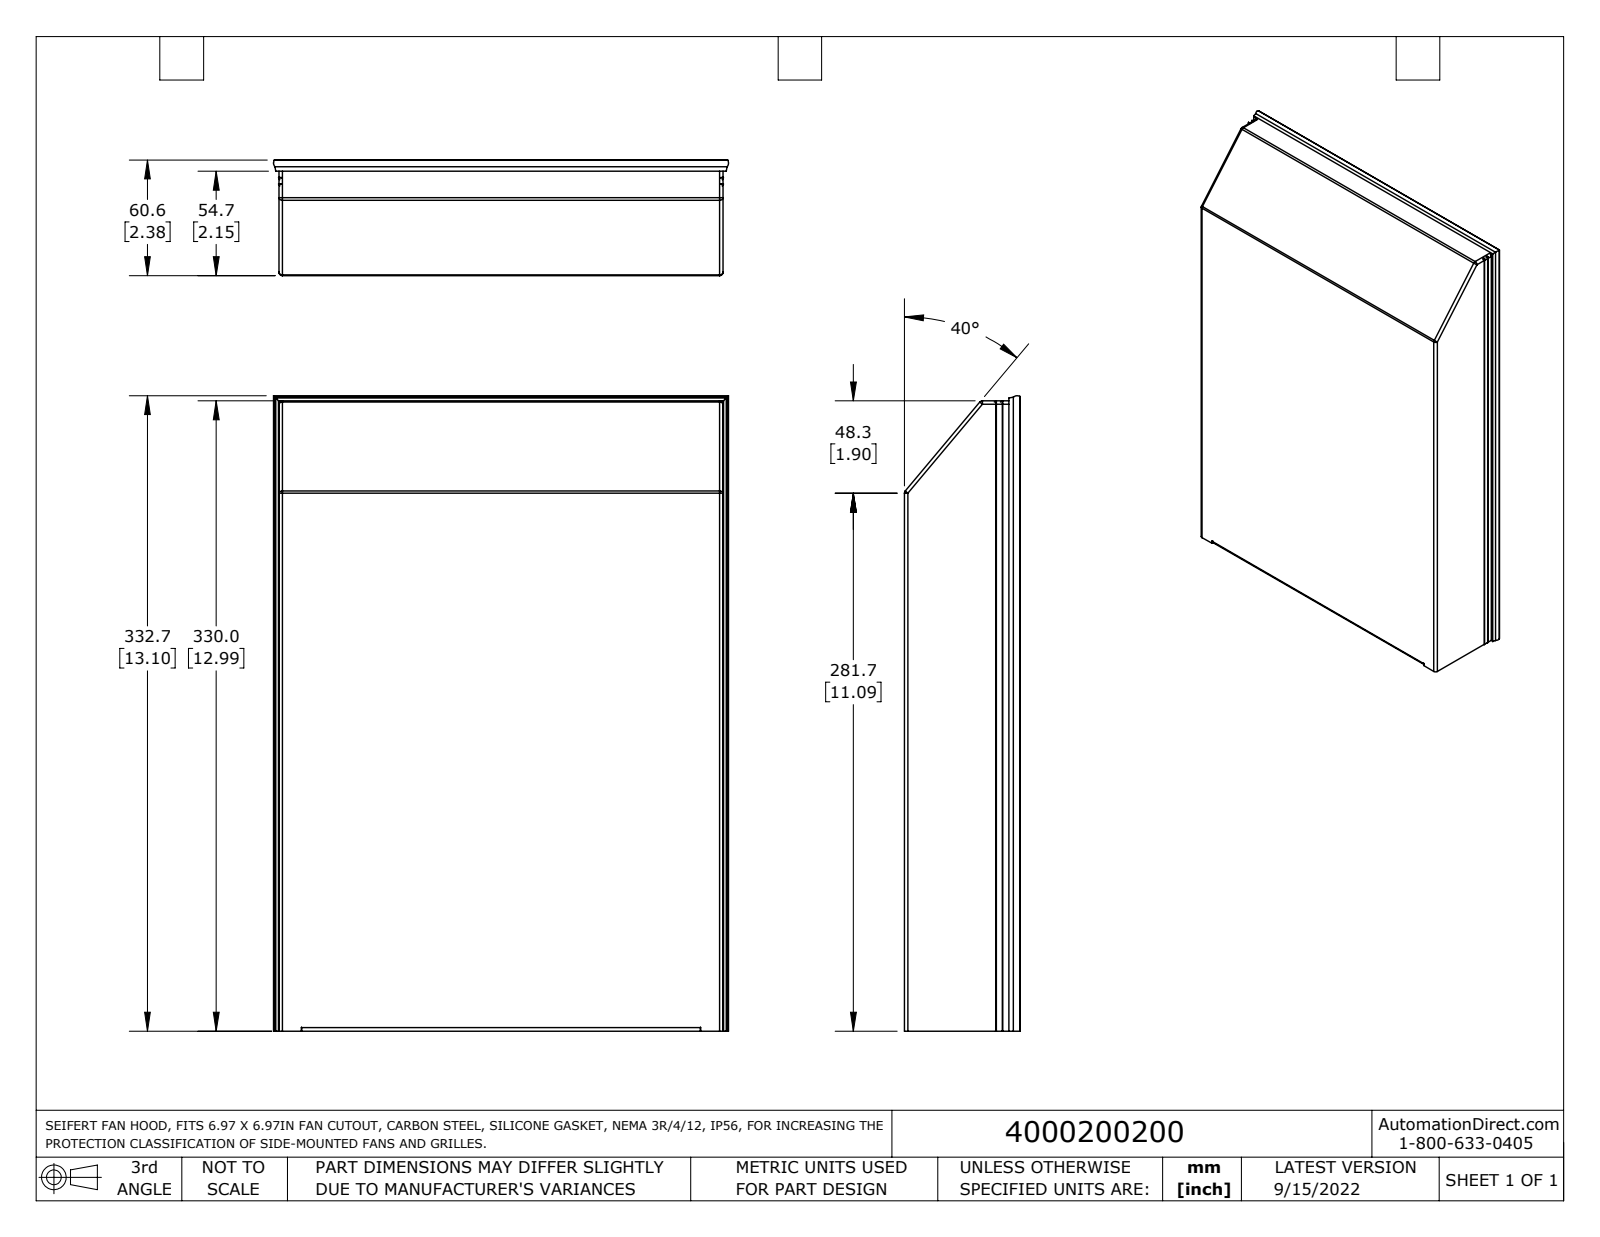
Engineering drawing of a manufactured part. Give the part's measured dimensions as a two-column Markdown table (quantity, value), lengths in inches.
| quantity | value |
| --- | --- |
| part name | 45391 |
| STEP written by | SolidWorks 2021 (AUTOMOTIVE_DESIGN) |
| units | inches |
| bodies | 4 solids, 307 faces (139 planar, 160 cylindrical, 8 other) |
| overall size | 13.098 × 9.386 × 2.384 |
| volume | 11.9 in³ |
| surface area | 538.1 in² |
| round holes (diameter × count) | 0.217 × 4 |
| partial cylindrical surfaces (radius × count) | 0.118 × 19, 0.004 × 12, 0.278 × 12, 1.181 × 12, 0.008 × 9, 0.031 × 9, 0.071 × 9, 0.039 × 6 |
| main face-to-face distances | 0.031, 9.126, 0.059, 8.78, 0.378, 0.346, 8.748, 0.437, 8.72, 0.406 |
| hole center spacings | 6.594, 9.488, 11.555 |
